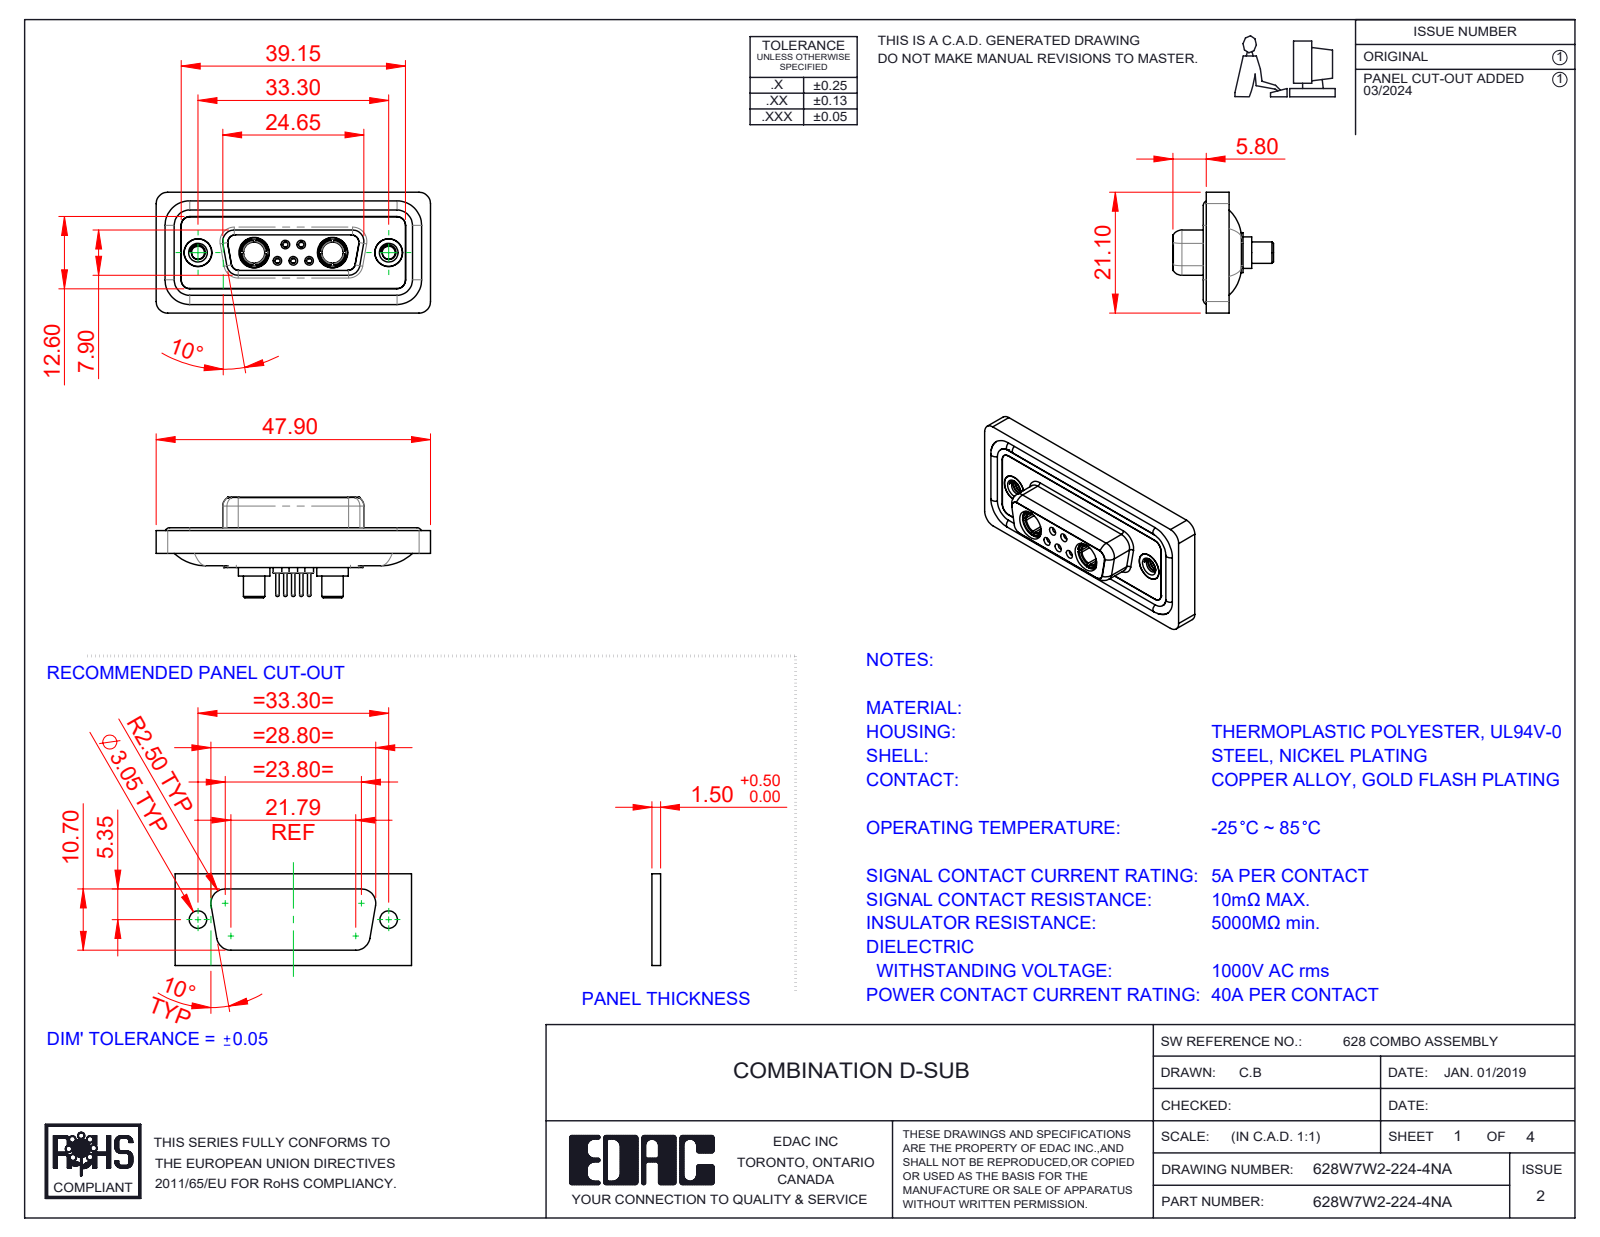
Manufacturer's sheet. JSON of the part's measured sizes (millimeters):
{"part_name": "628Combo Shell Front_15 Contacts; 628Combo Contact Row 1_24; Power Socket_40A S; 628Combo Contact Row 2_24 (+5 more)", "step_written_by": "SolidWorks 2023 (CONFIG_CONTROL_DESIGN)", "units": "millimeters", "bodies": {"solids": 16, "faces": 807, "planar": 238, "cylindrical": 331, "other": 238}, "overall_size": [47.9, 21.1, 17.55], "volume_mm3": 6116, "surface_area_mm2": 9904, "round_holes": [[0.9, 5], [1.1, 5], [1.5, 5], [2, 5], [4.85, 4], [1.6, 3], [1.7, 2], [2.26, 2], [3.7, 2], [4, 2], [4.05, 2], [5, 2]], "round_bosses_or_shafts": [[1.6, 6], [2.2, 5], [0.6, 5], [5.5, 2], [5.2, 2], [4.96, 2], [4.95, 2], [4.8, 2]], "partial_cylinders_radius": [[1.5, 22], [2, 20], [1.35, 12], [1.6, 8], [0.25, 4], [0.5, 4], [0.6, 4], [0.65, 4]], "face_to_face_distances": [0.4, 1.8, 1.6, 0.5, 2.9, 7.45, 1.1, 5.65, 6.6, 7.05], "hole_center_spacings": [3.16, 2.77, 9.8, 23.5, 4.31, 4.33, 5.03, 5.04]}
